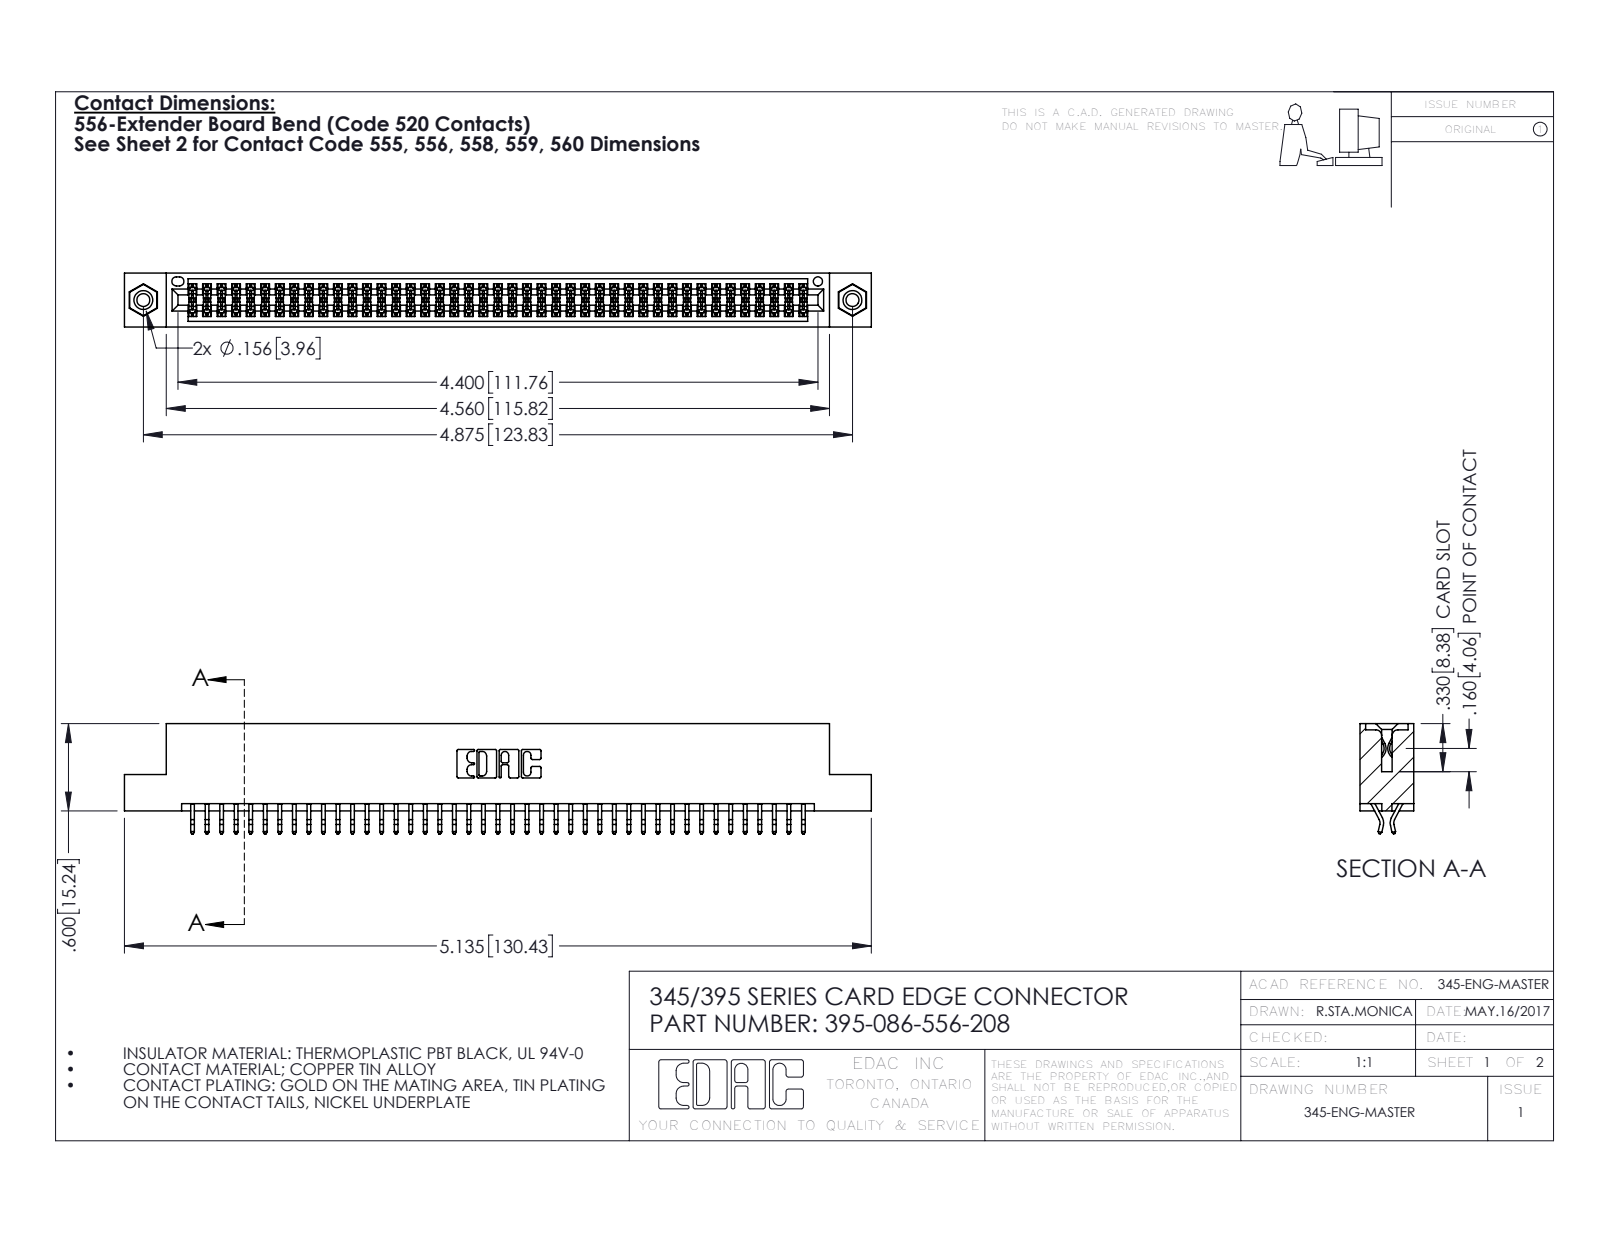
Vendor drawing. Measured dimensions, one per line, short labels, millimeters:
name: 345-250-001_345-250-003-102; 395-086-556-208; 345-292-001_556 Tail; 345 Part_Flush Mounting Lugs - 0.156 Dia-TI
written by: SolidWorks 2016 (CONFIG_CONTROL_DESIGN)
unit: mm
bodies: 89 solids, 5002 faces (3294 planar, 1692 cylindrical, 16 other)
size: 130.4 × 19.2 × 9.4
volume: 12 700 mm³; area: 18 680 mm²
holes: 2× ⌀2.3, 2× ⌀3.2, 2× ⌀4, 1× ⌀1.6
bosses: 2× ⌀3.9
rounds: 129× R0.2, 22× R0.3, 6× R0.2, 6× R0.8, 3× R0.7, 2× R0.3, 2× R0.4, 2× R0.5
face distances: 1.8, 7.6, 9.4, 5.1, 0.6, 2.5, 6.9, 5.7, 4.4, 3.8
hole spacings: 6.9, 117.8, 123.8
